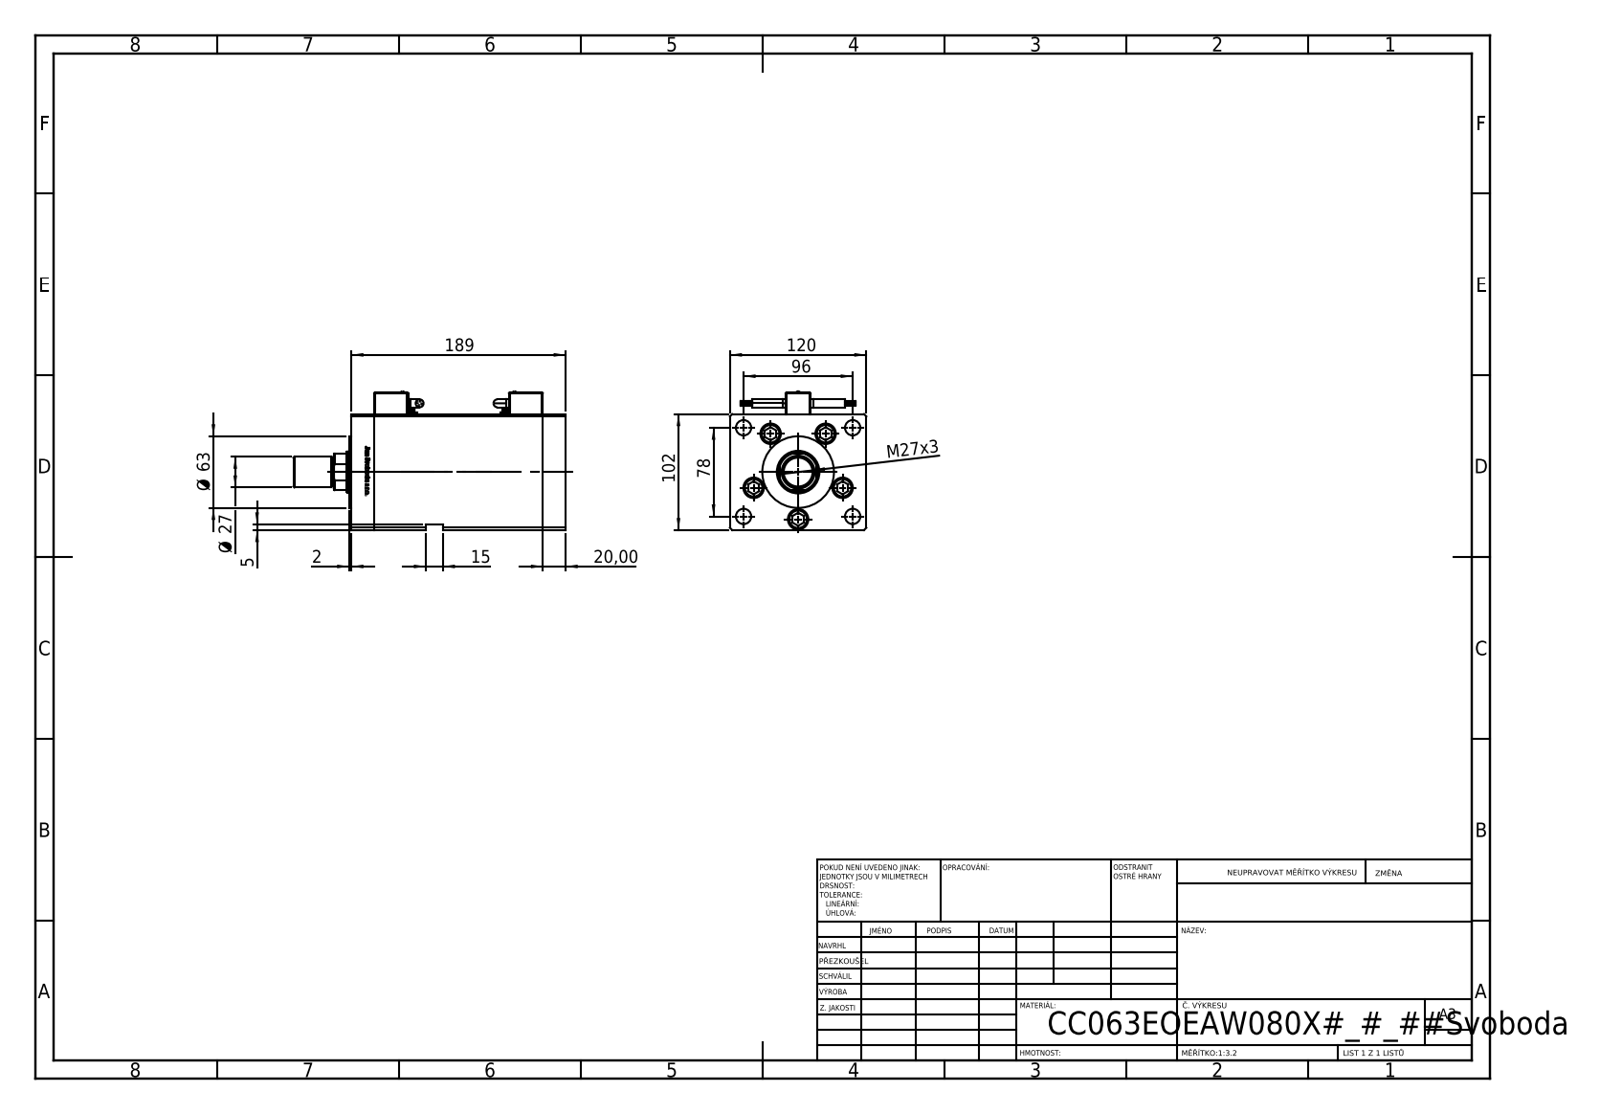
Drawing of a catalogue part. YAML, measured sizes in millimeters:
part_name: "V220CC_MALE_METRIC; V220C_E MIDDLE; ALLEN BOLT; V220C_FRONT_E (+3 more)"
step_written_by: "SolidWorks 2019 (CONFIG_CONTROL_DESIGN)"
units: millimeters
bodies: {solids: 17, faces: 1433, planar: 557, cylindrical: 260, other: 616}
overall_size: [239.5, 122.1, 120]
volume: 2030000
surface_area: 289554
round_holes:
  - {diameter: 13.5, count: 9}
  - {diameter: 18, count: 5}
  - {diameter: 12.5, count: 4}
  - {diameter: 18.5, count: 4}
  - {diameter: 2, count: 2}
  - {diameter: 3.6, count: 2}
  - {diameter: 5, count: 2}
  - {diameter: 7, count: 2}
  - {diameter: 13.16, count: 1}
  - {diameter: 25.5, count: 1}
  - {diameter: 36, count: 1}
  - {diameter: 37.5, count: 1}
round_bosses_or_shafts:
  - {diameter: 0.85, count: 8}
  - {diameter: 17, count: 5}
  - {diameter: 8, count: 5}
  - {diameter: 7, count: 4}
  - {diameter: 6, count: 2}
  - {diameter: 3.5, count: 2}
  - {diameter: 2.5, count: 2}
  - {diameter: 63, count: 1}
partial_cylinders:
  - {radius: 1, count: 24}
  - {radius: 4, count: 4}
  - {radius: 0.93, count: 2}
  - {radius: 6.58, count: 1}
  - {radius: 17.5, count: 1}
face_to_face_distances: [120, 20, 148.5, 168.5, 102, 34.25, 188.5, 14.25, 134.25, 154.25]
hole_center_spacings: [41.5, 61.85, 8.25, 24.39, 26.69, 45.54, 47.51, 47.92]
